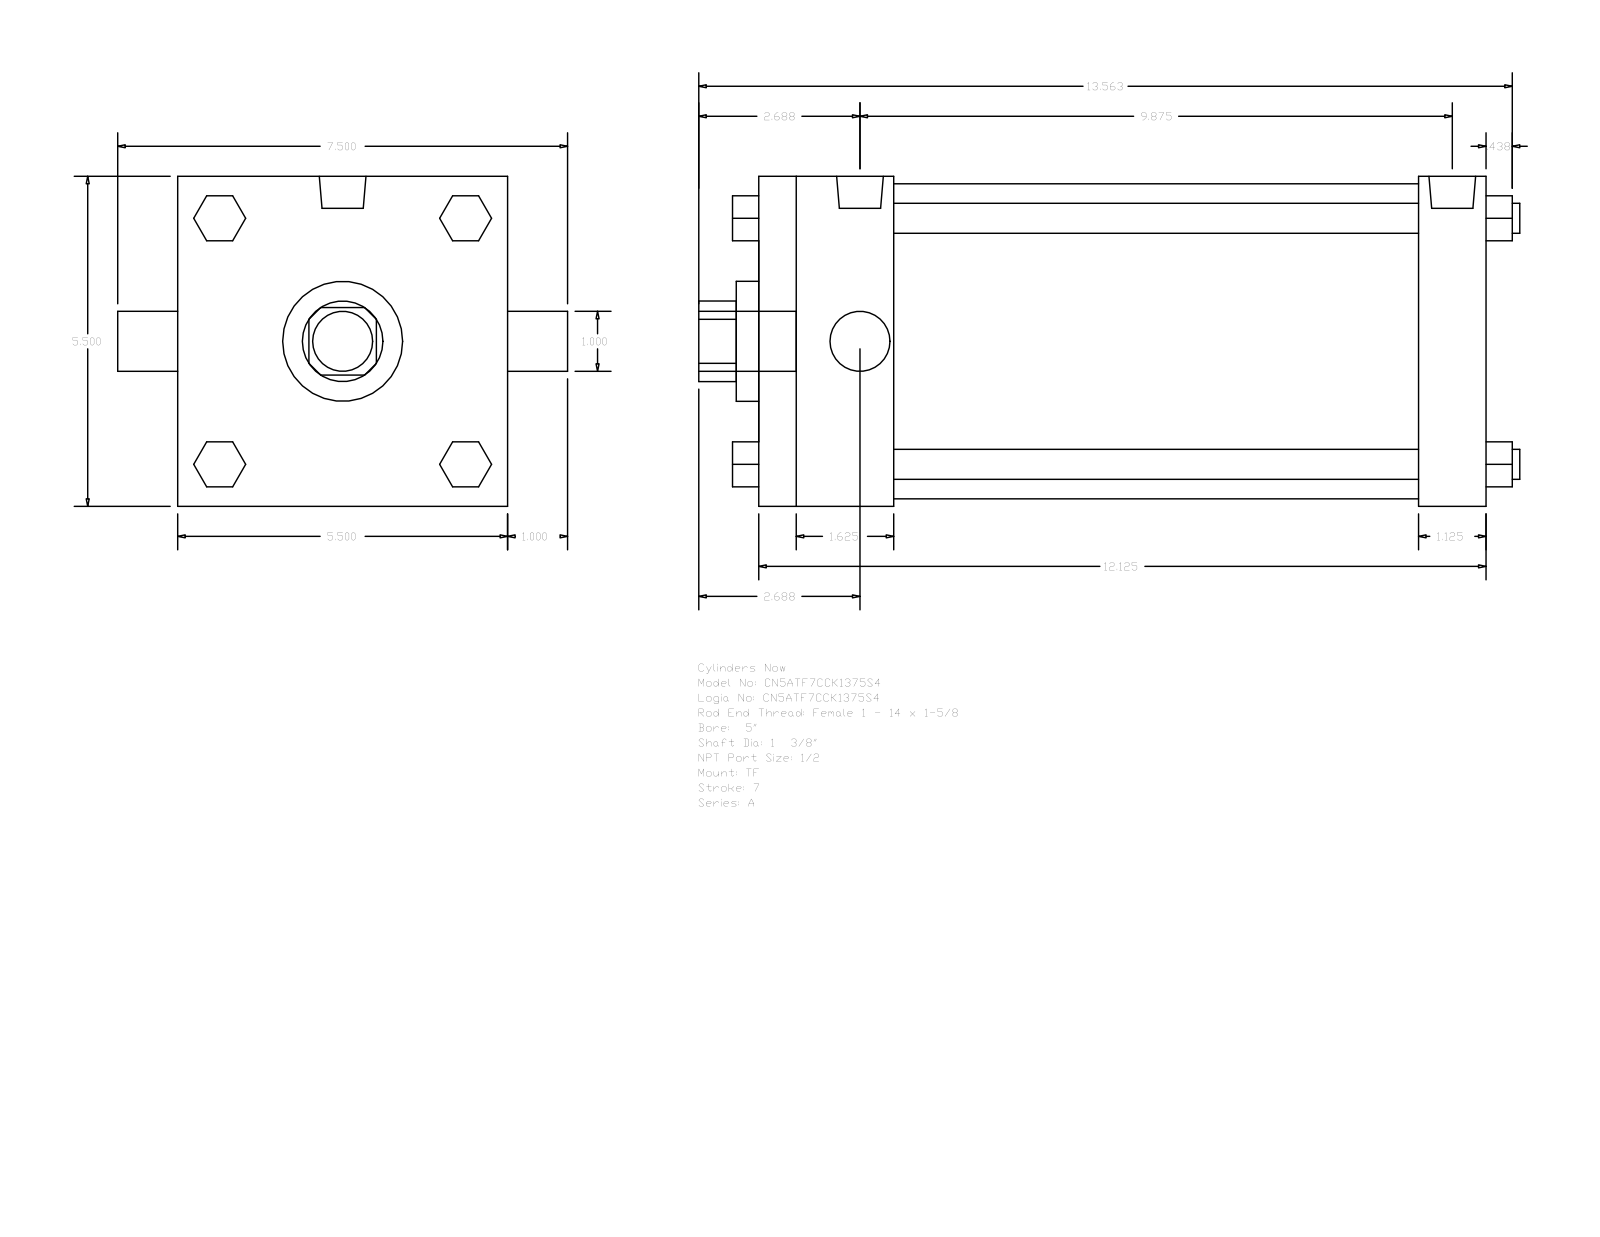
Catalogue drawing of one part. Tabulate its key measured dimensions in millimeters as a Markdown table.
| quantity | value |
| --- | --- |
| part name | A_TF__0500_1.375 |
| STEP written by | GSSL Pune (CONFIG_CONTROL_DESIGN) |
| units | millimeters |
| bodies | 0 solids, 120 faces (92 planar, 28 cylindrical, 0 other) |
| overall size | 347.66 × 190.5 × 139.7 |
| round holes (diameter × count) | 25.4 × 1, 34.92 × 1, 50.8 × 1, 133.35 × 1 |
| round bosses / shafts (diameter × count) | 12.7 × 4, 8.73 × 3, 19.77 × 2, 25.4 × 1 |
| partial cylindrical surfaces (radius × count) | 17.06 × 1 |
| main face-to-face distances | 139.7, 307.98, 28.58, 279.4, 57.15, 222.25, 250.83, 19.05, 52.07, 90.18 |
